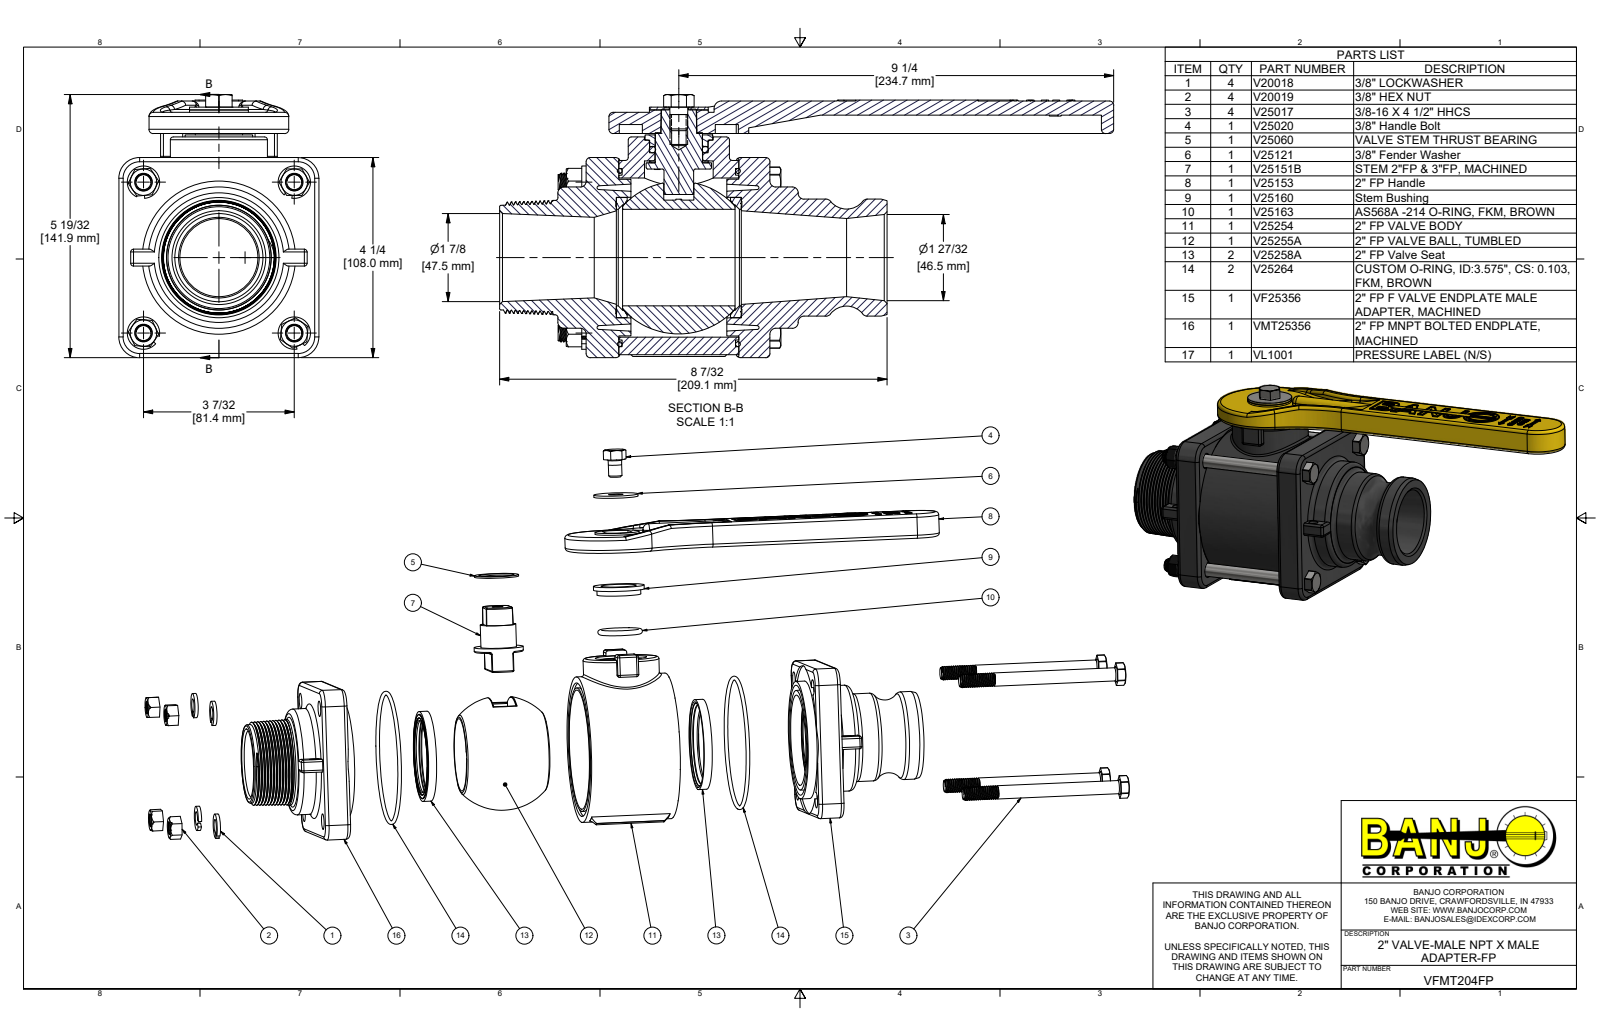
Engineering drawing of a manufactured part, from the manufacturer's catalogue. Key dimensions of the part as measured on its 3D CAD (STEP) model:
Part name (STEP PRODUCT): VFMT204FP; V25254; VL1001-D4.125; V20018 (+8 more)
STEP written by: Autodesk Inventor 2017 (AUTOMOTIVE_DESIGN)
Units: millimetres
Bodies: 28 solids, 1738 faces (664 planar, 494 cylindrical, 580 other)
Overall size (bounding box): 331.44 × 141.94 × 107.95
Volume: 1 054 000 mm³ · Surface area: 294 628 mm²
Round holes (diameter × count): ⌀4.33 ×12, ⌀6.6 ×4, ⌀7.81 ×4, ⌀9.78 ×4, ⌀11.18 ×4, ⌀7.8 ×1, ⌀10.31 ×1, ⌀17.29 ×1, ⌀24.43 ×1, ⌀25.4 ×1, ⌀25.81 ×1, ⌀31.62 ×1
Round bosses / shafts (diameter × count): ⌀8.24 ×60, ⌀9.52 ×5, ⌀17.46 ×4, ⌀88.9 ×1, ⌀84.58 ×1, ⌀84.45 ×1, ⌀76.2 ×1, ⌀75.41 ×1
Partial cylindrical surfaces — rounded edges, fillets, slot ends (radius × count): R1.52 ×24, R2.29 ×24, R0.76 ×12, R0.81 ×10, R4.12 ×8, R3.97 ×6, R8.12 ×4, R11.18 ×4
Main face-to-face distances: 17.66, 99.19, 81.53, 107.94, 1.53, 6.61, 35.17, 72.77, 7.62, 1.33
Hole centre spacings: 50.22, 71.02, 97.02, 25.99, 28.77, 54.26, 76.38, 86.98
